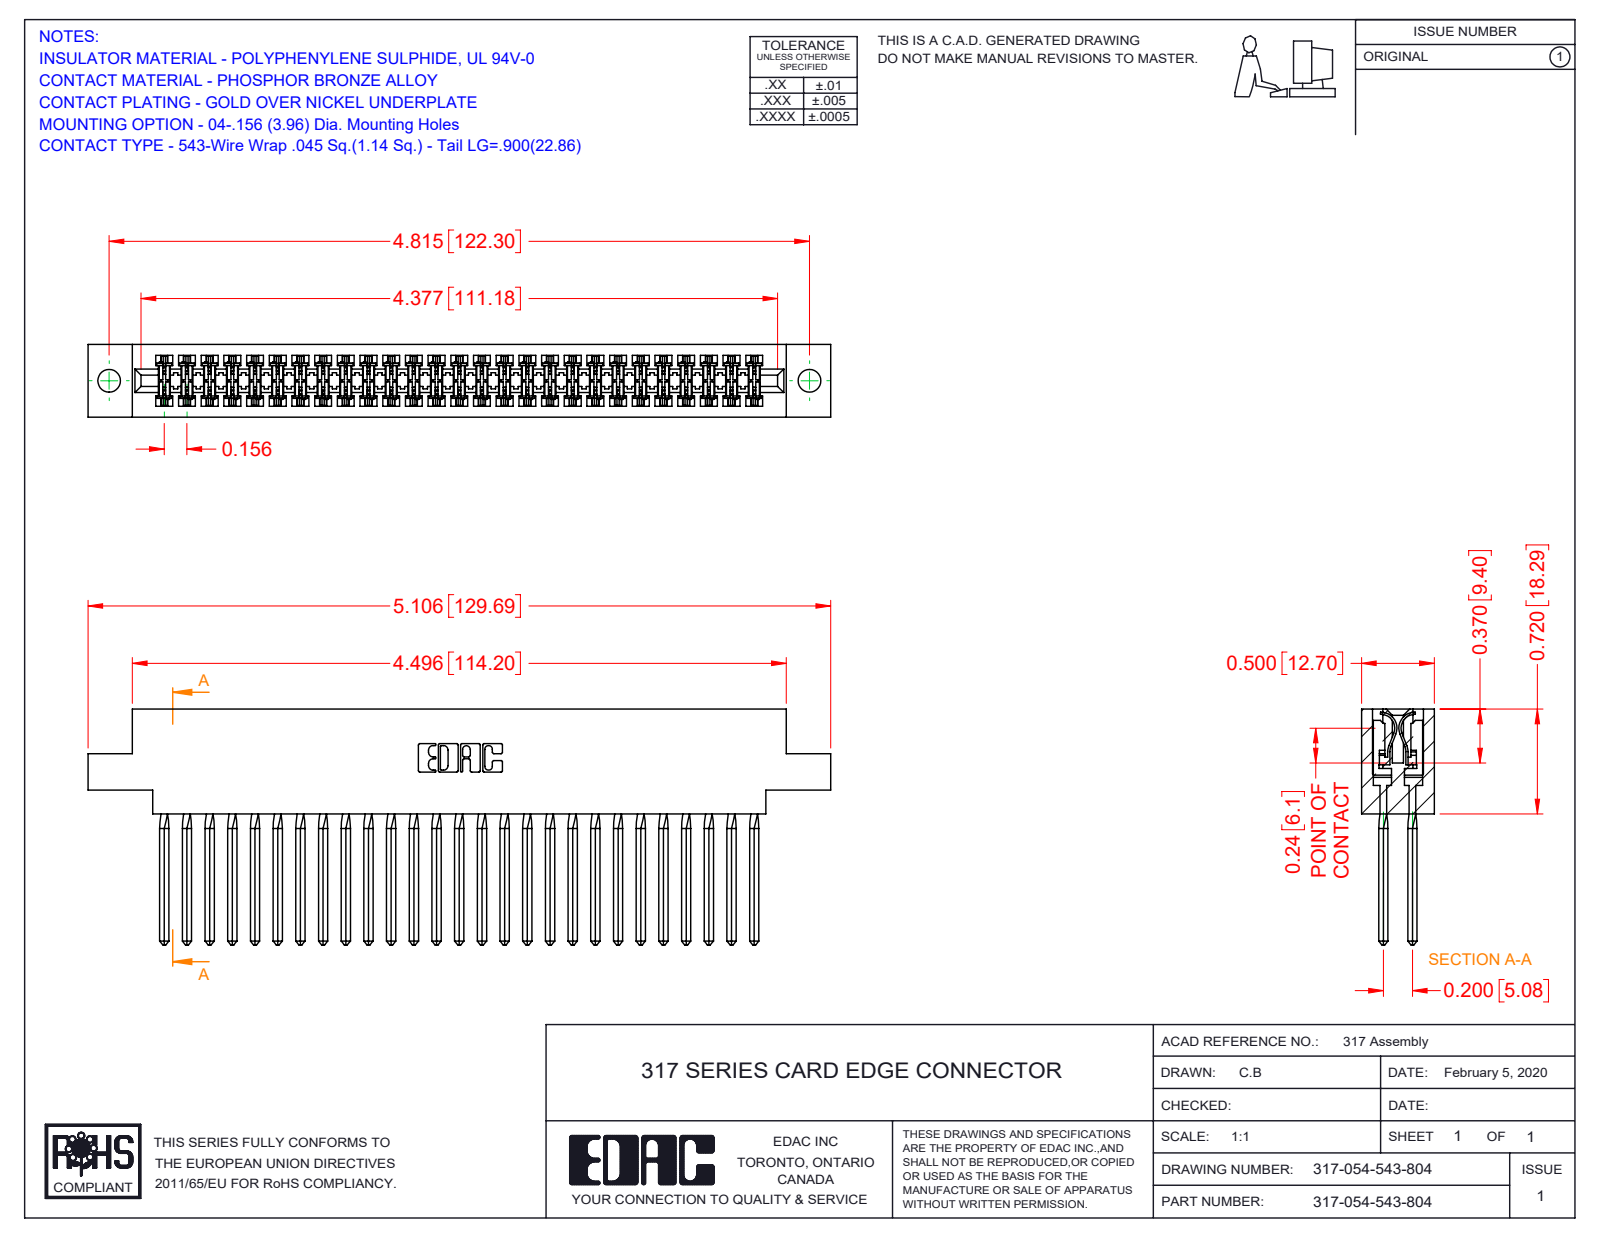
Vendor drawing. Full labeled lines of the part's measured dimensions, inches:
Part name (STEP PRODUCT): 317 Part_.156 Dia - TH; 317-054-543-804; 317-290-001_543
STEP written by: SolidWorks 2016 (CONFIG_CONTROL_DESIGN)
Units: inches
Bodies: 55 solids, 4908 faces (4000 planar, 692 cylindrical, 216 other)
Overall size (bounding box): 5.106 × 1.62 × 0.5
Volume: 1.308 in³ · Surface area: 49.23 in²
Round holes (diameter × count): ⌀0.156 ×2
Partial cylindrical surfaces — rounded edges, fillets, slot ends (radius × count): R0.015 ×108, R0.01 ×22, R0.007 ×6, R0.031 ×6, R0.026 ×3, R0.095 ×2, R0.1 ×2, R0.11 ×2
Main face-to-face distances: 0.5, 0.075, 0.425, 0.35, 0.11, 0.195, 0.094, 0.72, 0.2, 0.115
Hole centre spacings: 4.815
